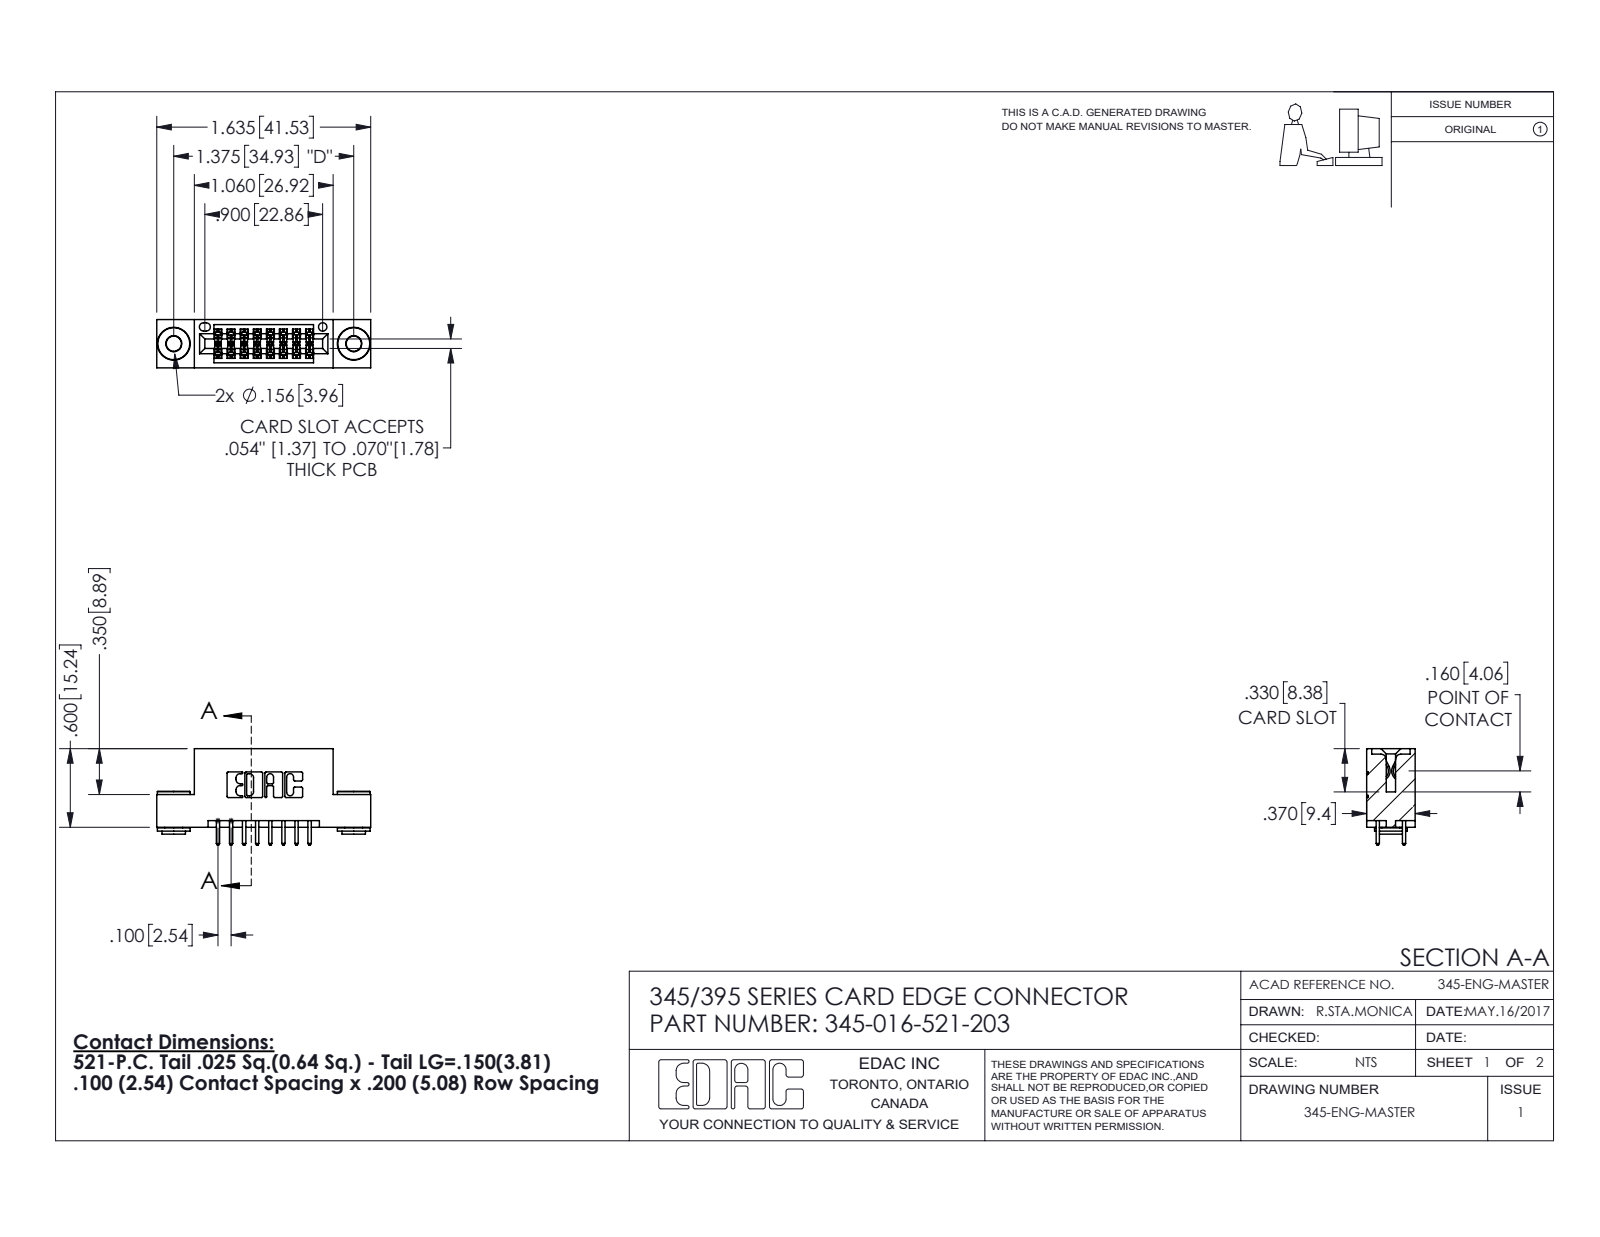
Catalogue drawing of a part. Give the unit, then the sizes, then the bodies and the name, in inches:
Units: inches
Overall size (bounding box): 1.635 × 0.737 × 0.37
Round holes (diameter × count): ⌀0.116 ×2, ⌀0.156 ×2, ⌀0.064 ×1
Round bosses / shafts (diameter × count): ⌀0.25 ×2, ⌀0.18 ×2, ⌀0.136 ×2
Partial cylindrical surfaces — rounded edges, fillets, slot ends (radius × count): R0.006 ×24, R0.01 ×22, R0.01 ×16, R0.007 ×6, R0.031 ×6, R0.026 ×3, R0.014 ×2, R0.019 ×2
Main face-to-face distances: 0.2, 0.072, 0.298, 0.37, 0.1, 0.025, 0.3, 0.098, 0.272, 0.225
Hole centre spacings: 0.27, 1.144, 1.375
Volume: 0.228 in³ · Surface area: 7.78 in²
Bodies: 19 solids, 964 faces (618 planar, 338 cylindrical, 8 other)
Part name (STEP PRODUCT): 345-250-002_345-250-002-102; 345 Part_Flush Mounting Lugs - 0.156 Dia-TH; 345-292-001_345-293-121; 345-016-521-203
STEP written by: SolidWorks 2016 (CONFIG_CONTROL_DESIGN)
